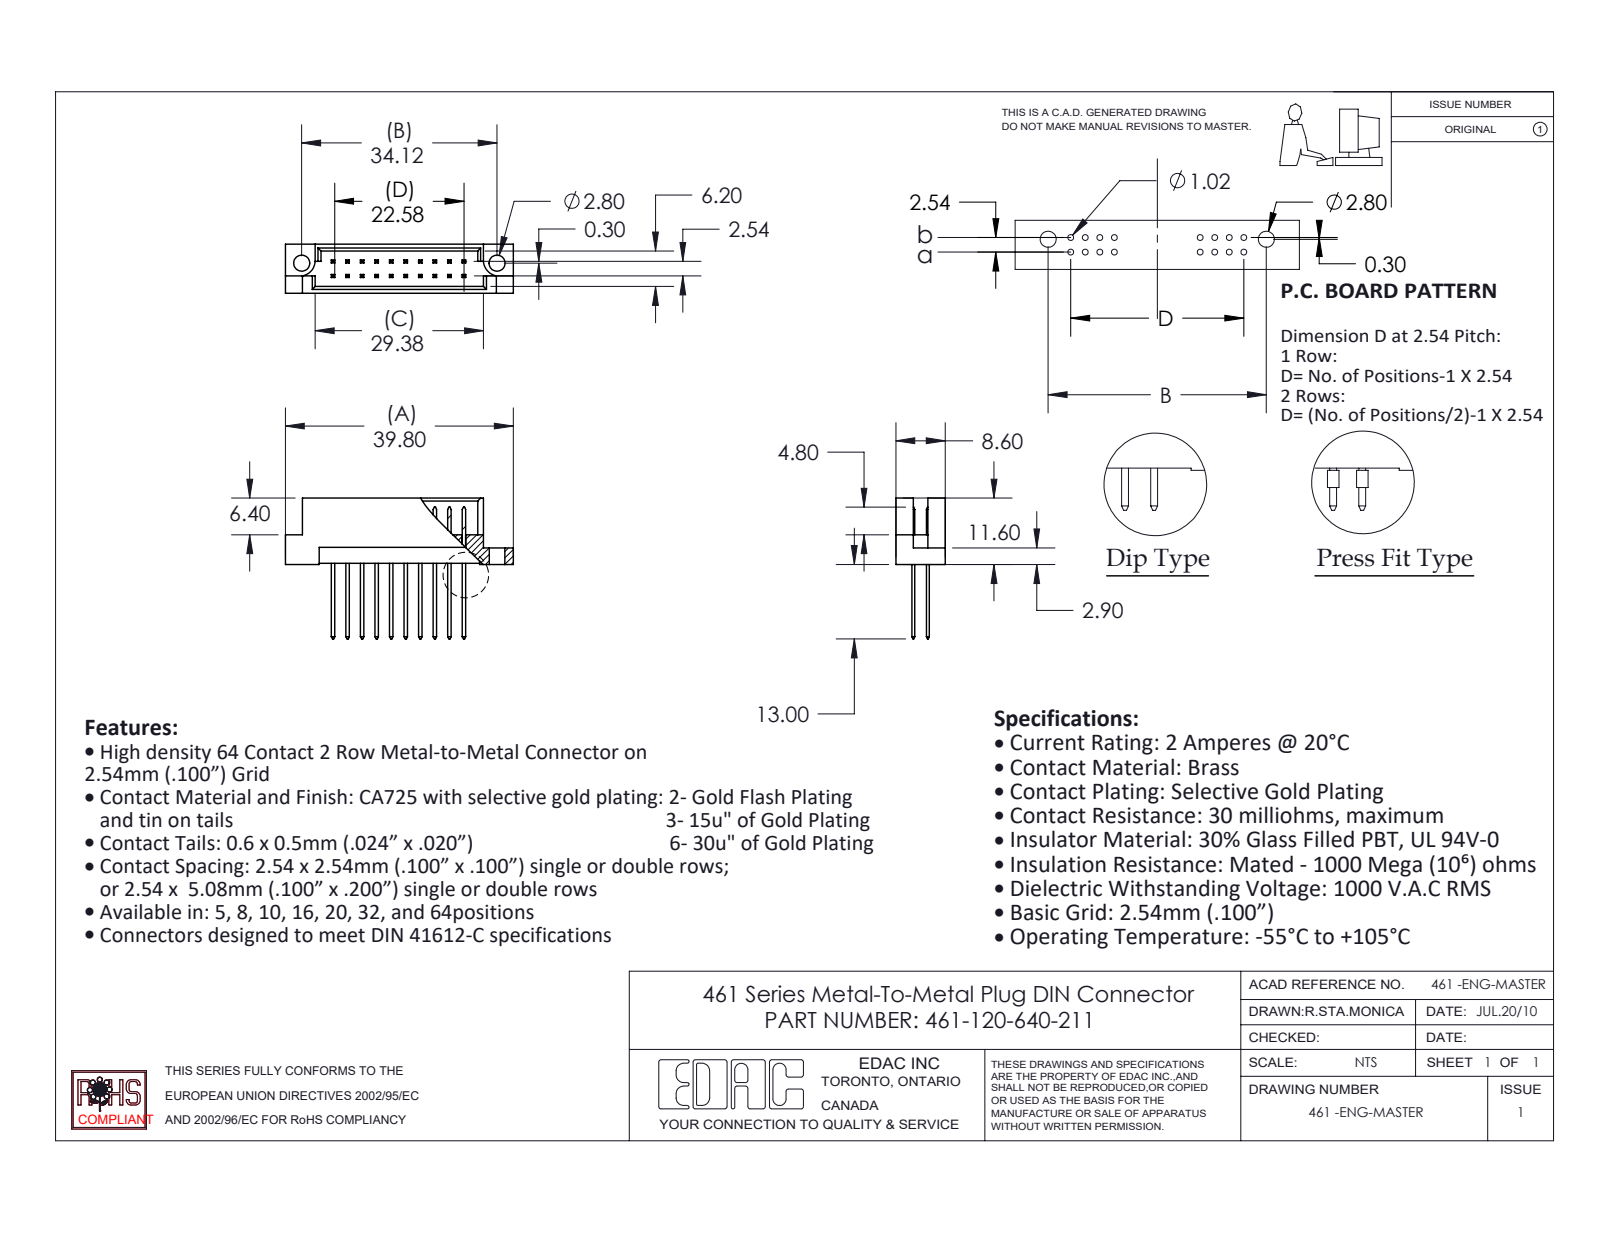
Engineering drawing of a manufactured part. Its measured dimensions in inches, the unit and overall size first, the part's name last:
Units: inches
Overall size (bounding box): 1.567 × 0.969 × 0.339
Round holes (diameter × count): ⌀0.11 ×2
Partial cylindrical surfaces — rounded edges, fillets, slot ends (radius × count): R0.11 ×2
Main face-to-face distances: 0.1, 0.047, 0.291, 0.339, 0.129, 0.209, 0.082, 0.162, 0.109, 0.229
Hole centre spacings: 1.343
Volume: 0.124 in³ · Surface area: 5.18 in²
Bodies: 21 solids, 408 faces (402 planar, 6 cylindrical, 0 other)
Part name (STEP PRODUCT): 461-290_40; 461 Part_20; 461-120-640-211
STEP written by: SolidWorks 2020 (CONFIG_CONTROL_DESIGN)
